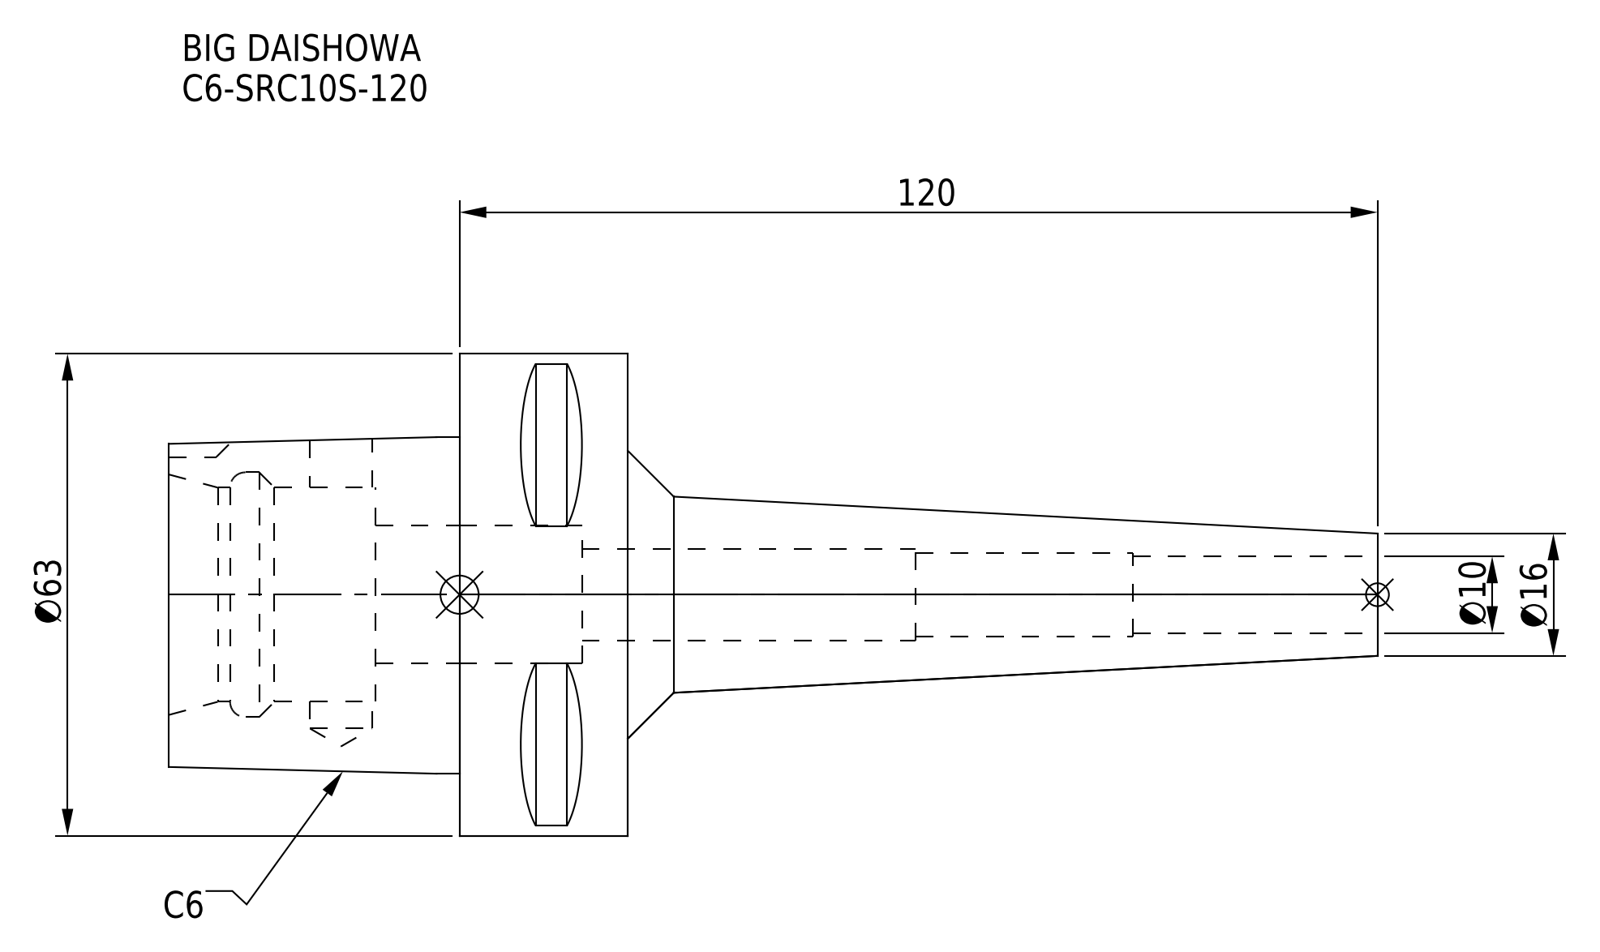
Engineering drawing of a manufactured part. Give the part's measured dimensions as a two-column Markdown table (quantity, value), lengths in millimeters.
| quantity | value |
| --- | --- |
| part name | C6-SRC10S-120 |
| STEP written by | CREO PARAMETRIC BY PTC INC, 2016380 (AUTOMOTIVE_DESIGN) |
| units | millimeters |
| bodies | 1 solid, 65 faces (30 planar, 21 cylindrical, 14 other) |
| overall size | 158 × 63 × 63 |
| volume | 123 101 mm³ |
| surface area | 29 581 mm² |
| round holes (diameter × count) | 8.1 × 1, 10 × 1, 11 × 1, 12 × 1, 18 × 1, 28 × 1, 32 × 1 |
| round bosses / shafts (diameter × count) | 63 × 1 |
| partial cylindrical surfaces (radius × count) | 5 × 1 |
| main face-to-face distances | 22, 27, 60, 38, 33, 11, 24.89, 55.4, 6, 16 |
